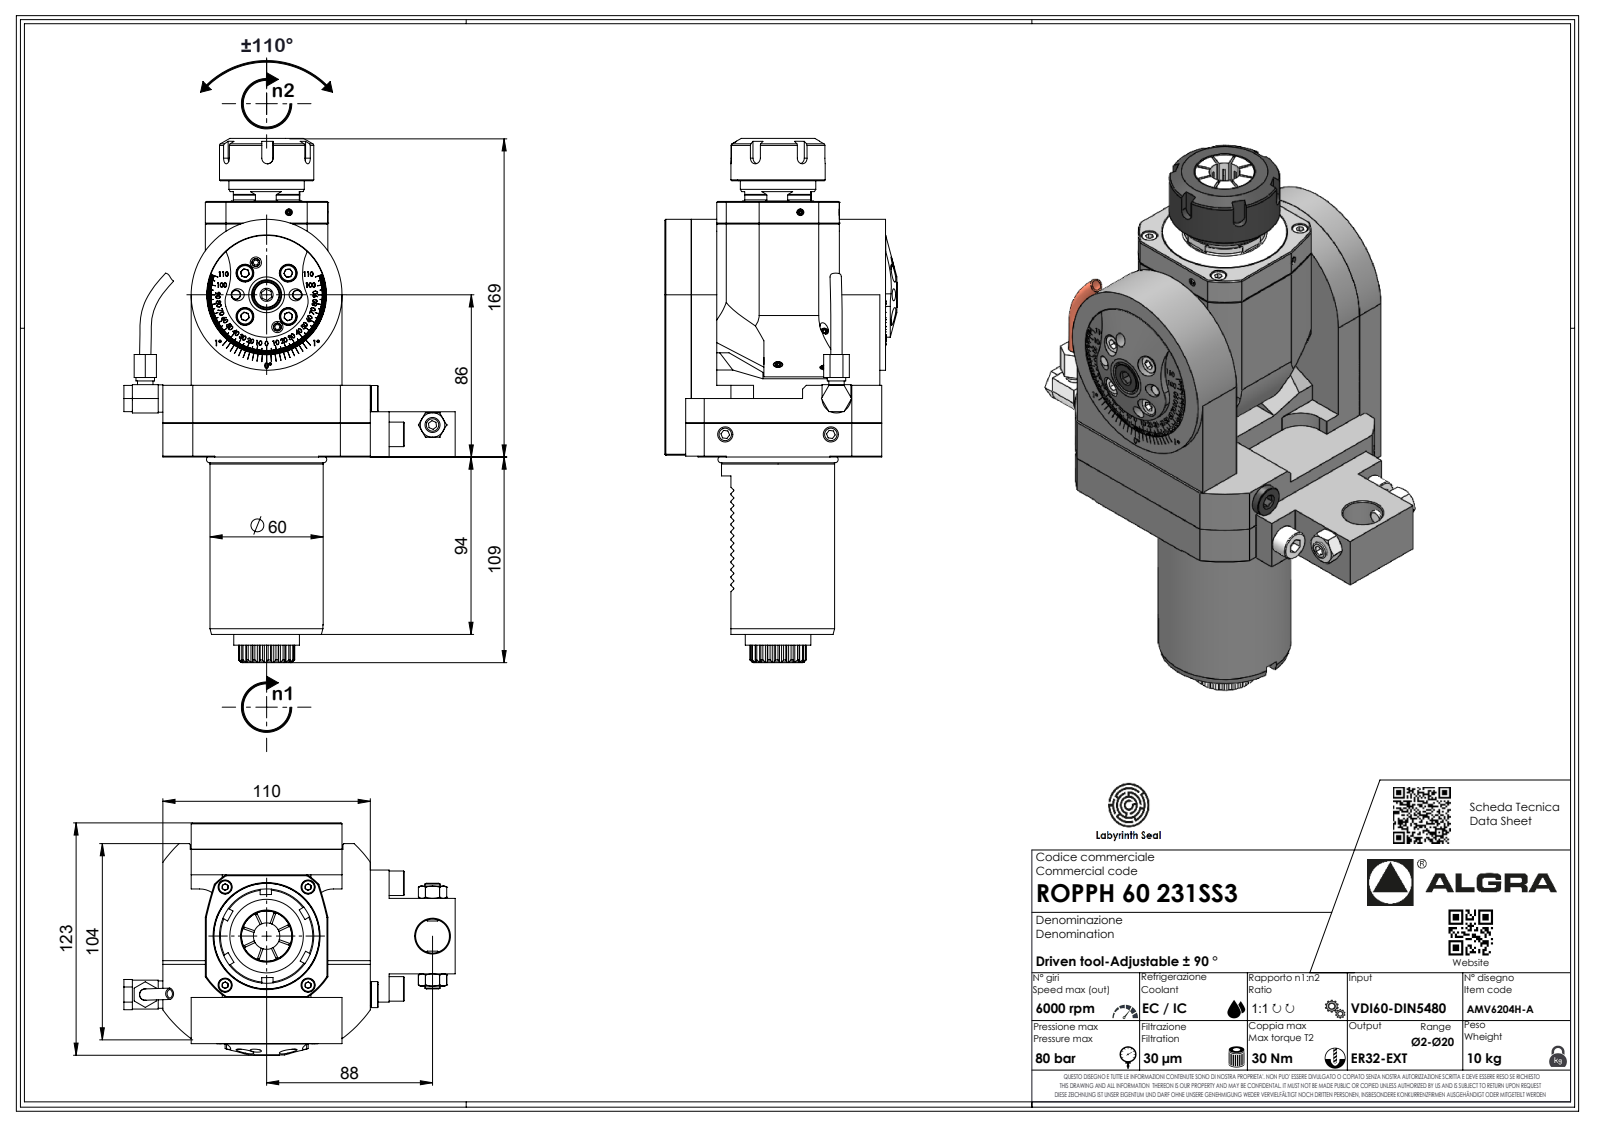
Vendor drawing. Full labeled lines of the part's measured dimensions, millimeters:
Part name (STEP PRODUCT): ROPPH60231SS3
STEP written by: SolidWorks 2023 (AUTOMOTIVE_DESIGN)
Units: millimetres
Bodies: 1 solid, 927 faces (589 planar, 166 cylindrical, 172 other)
Overall size (bounding box): 277.91 × 175.7 × 123
Volume: 1 237 000 mm³ · Surface area: 124 065 mm²
Round holes (diameter × count): ⌀2.1 ×1, ⌀50 ×1
Round bosses / shafts (diameter × count): ⌀80 ×1, ⌀60 ×1, ⌀58.7 ×1, ⌀40 ×1, ⌀34.8 ×1, ⌀14.5 ×1, ⌀9.8 ×1, ⌀8.2 ×1
Partial cylindrical surfaces — rounded edges, fillets, slot ends (radius × count): R0.3 ×14, R0.33 ×7, R0.52 ×7, R3.7 ×7, R3 ×5, R0.2 ×3, R10 ×2, R12 ×2
Main face-to-face distances: 22.5, 87.5, 65, 80, 7.5, 95, 15, 7, 135.5, 27.5
